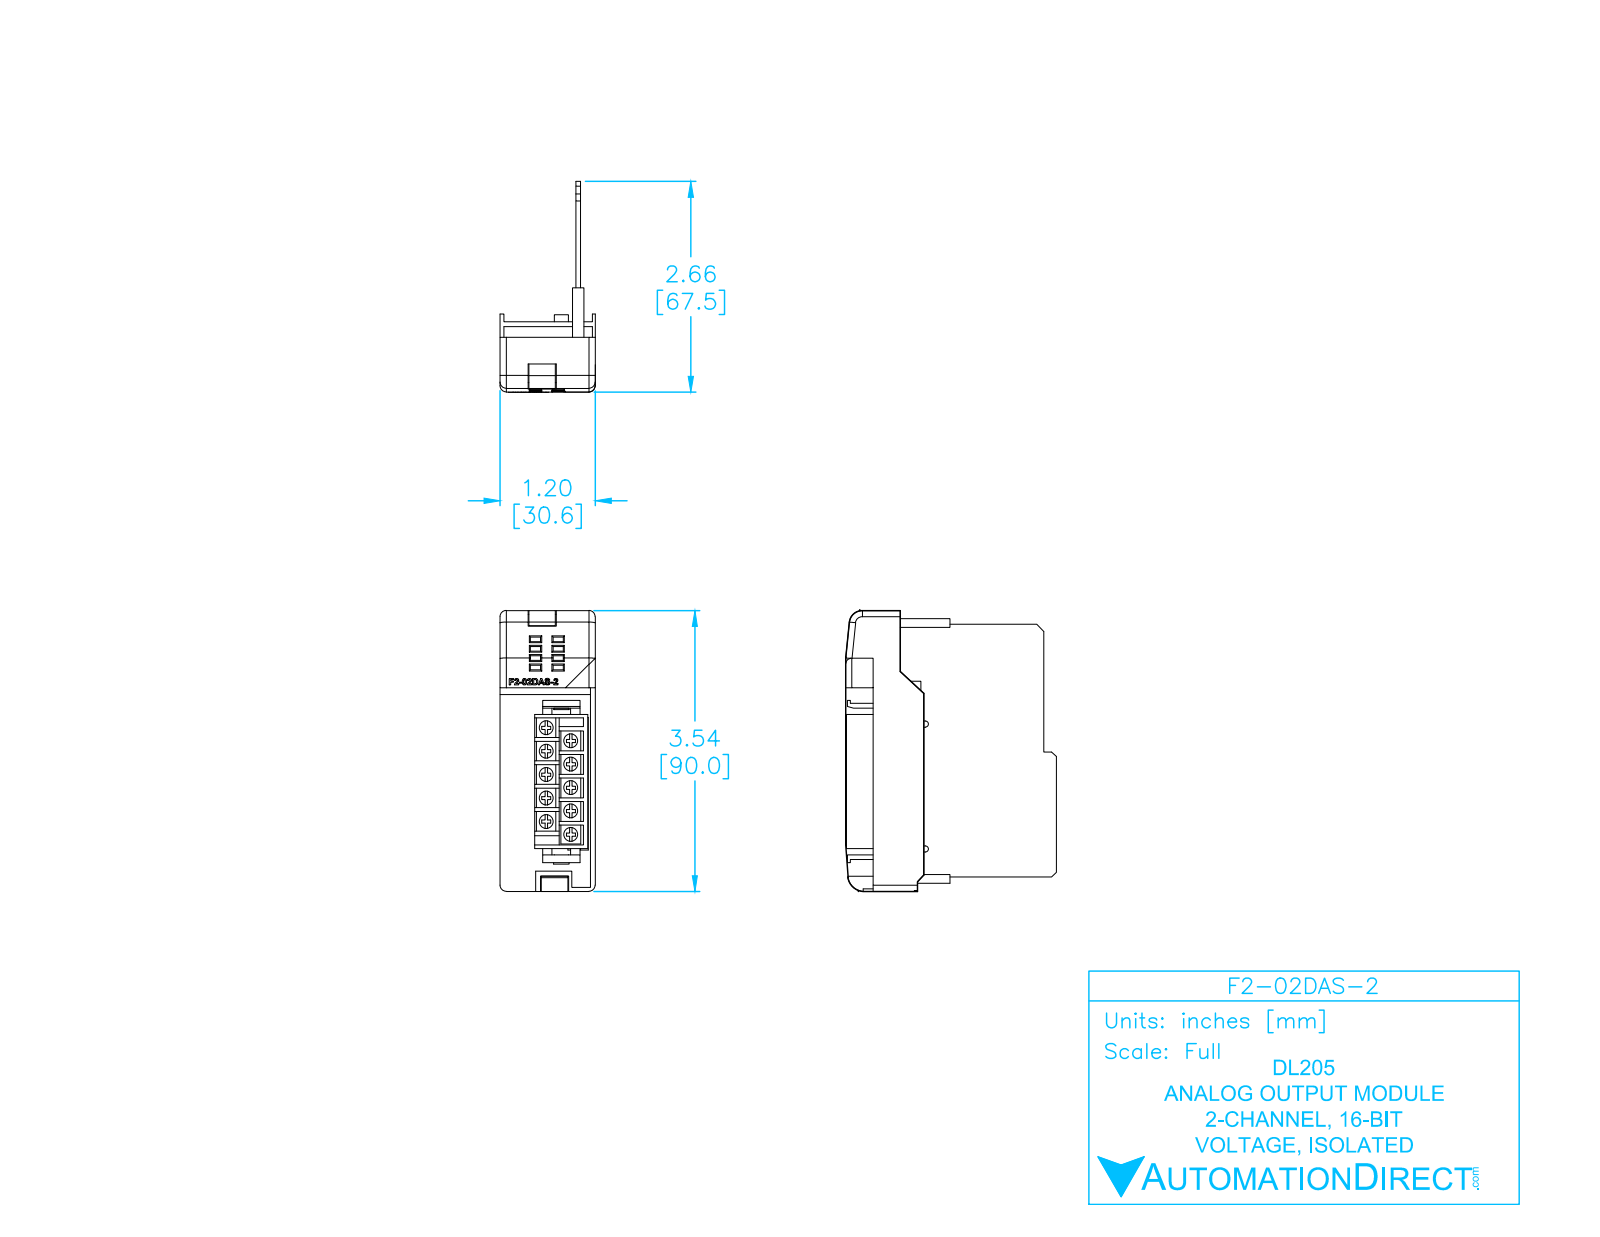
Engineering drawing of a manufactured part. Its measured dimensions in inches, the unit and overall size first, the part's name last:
Units: inches
Overall size (bounding box): 3.543 × 2.66 × 1.203
Round bosses / shafts (diameter × count): ⌀0.177 ×10
Partial cylindrical surfaces — rounded edges, fillets, slot ends (radius × count): R0.014 ×16, R0.079 ×9, R0.01 ×2, R0.039 ×2, R0.049 ×2, R0.162 ×1, R0.212 ×1
Main face-to-face distances: 0.059, 0.186, 0.245, 0.093, 0.152, 0.093, 0.127, 0.033, 0.32, 0.956
Volume: 1.547 in³ · Surface area: 44.14 in²
Bodies: 6 solids, 596 faces (414 planar, 75 cylindrical, 107 other)
Part name (STEP PRODUCT): F2-02DAS-2_ModuleCase_light_NEW
STEP written by: SolidWorks 2009 (AUTOMOTIVE_DESIGN)
